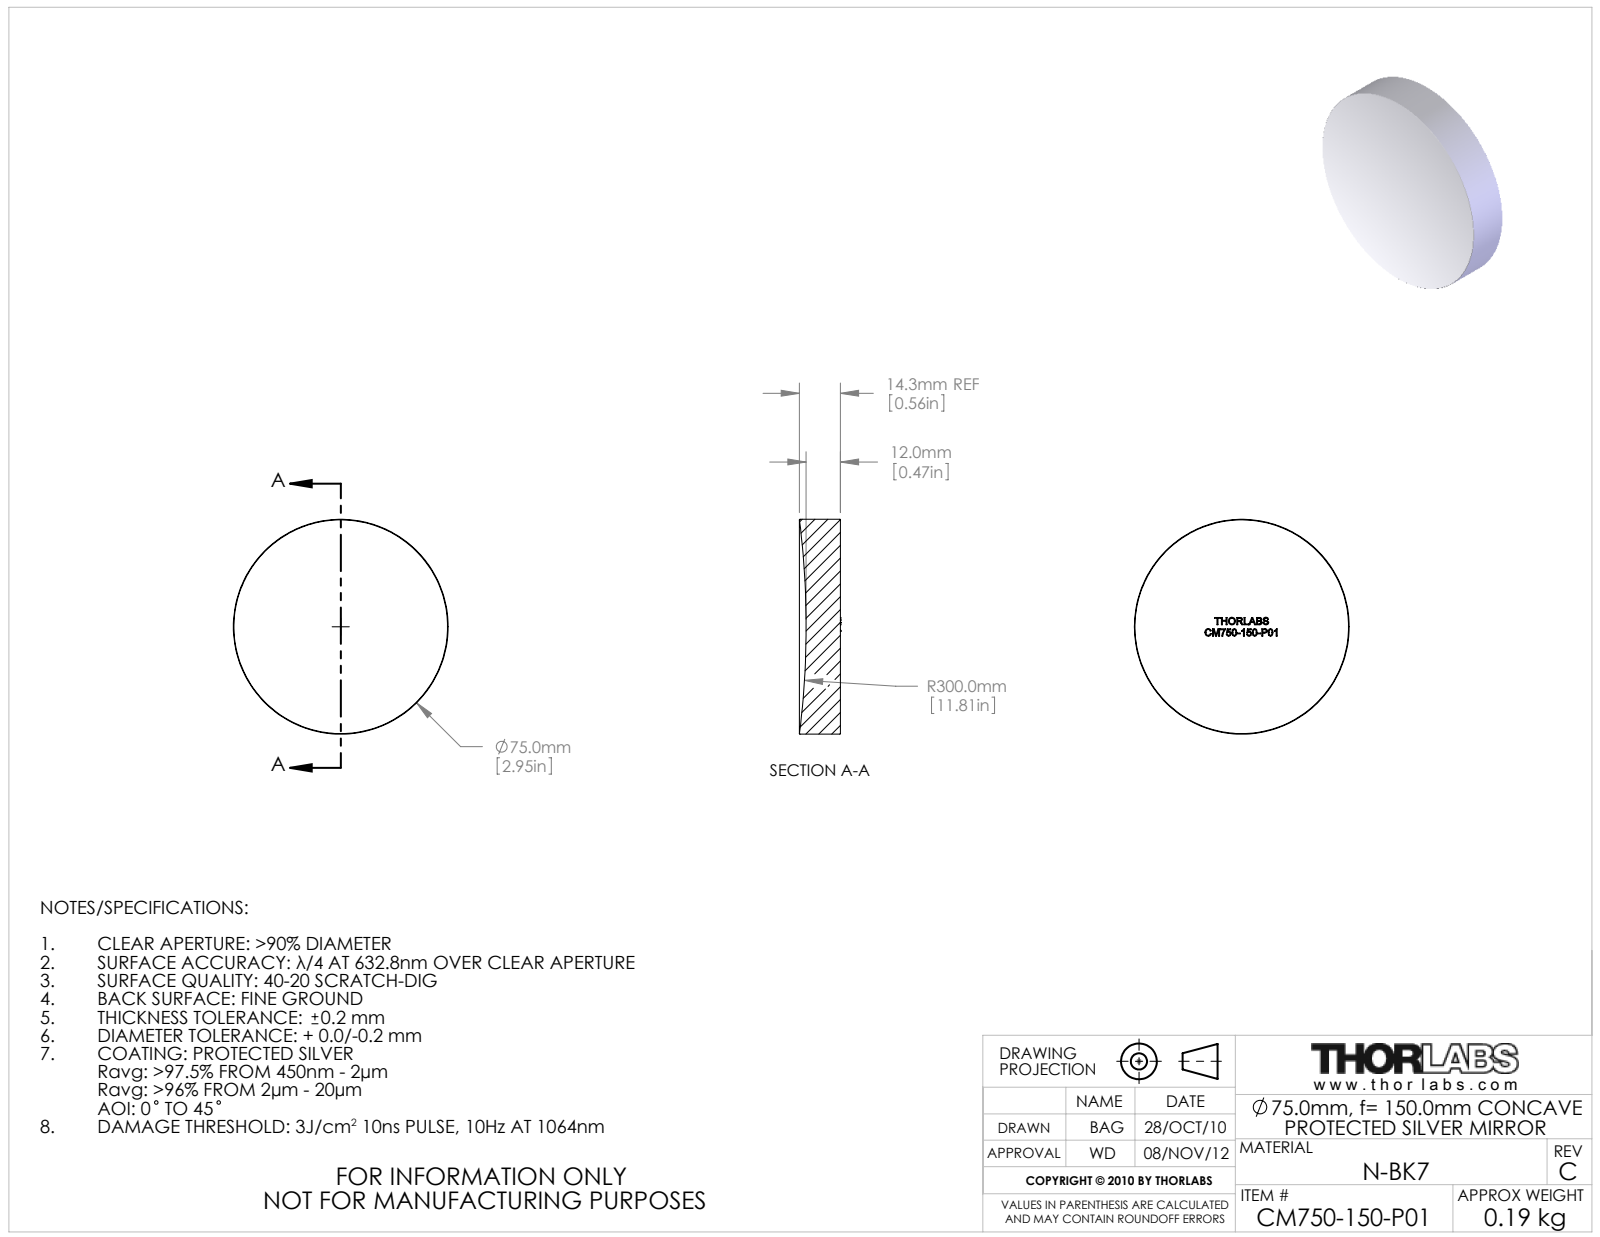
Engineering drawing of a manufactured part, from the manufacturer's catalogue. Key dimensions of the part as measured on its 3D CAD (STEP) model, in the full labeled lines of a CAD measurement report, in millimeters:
Part name (STEP PRODUCT): 17576-E0W
STEP written by: SolidWorks 2009 (AUTOMOTIVE_DESIGN)
Units: millimetres
Bodies: 1 solid, 271 faces (150 planar, 2 cylindrical, 119 other)
Overall size (bounding box): 75 × 75 × 14.3
Volume: 58 190 mm³ · Surface area: 12 170 mm²
Round bosses / shafts (diameter × count): ⌀75 ×1
Main face-to-face distances: 2.6, 0.4, 0.4, 2.3, 0.3, 4.7, 4, 2, 1.5, 4
